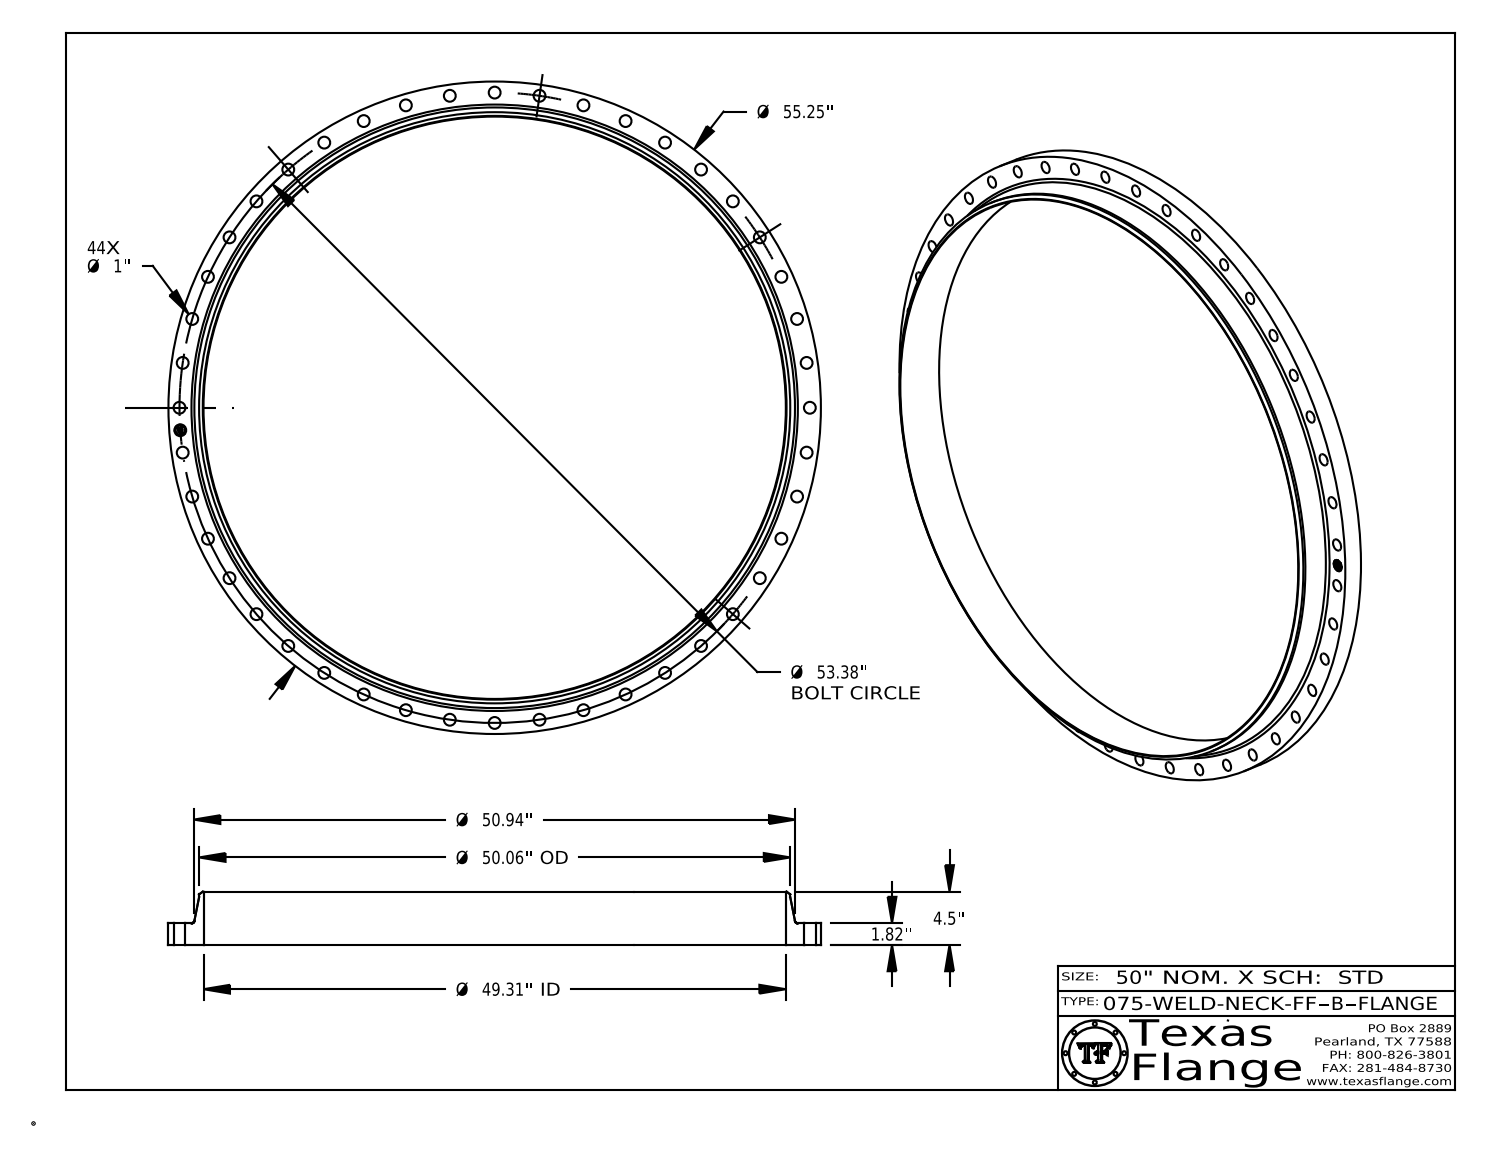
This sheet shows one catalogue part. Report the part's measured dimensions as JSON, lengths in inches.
{"part_name": "075-WELD-NECK-FF, Series B", "step_written_by": "CATIA V5 STEP AP214 (AUTOMOTIVE_DESIGN)", "units": "inches", "bodies": {"solids": 1, "faces": 488, "planar": 368, "cylindrical": 114, "other": 6}, "overall_size": [55.25, 55.25, 4.5], "volume_in3": 1054, "surface_area_in2": 2497, "round_holes": [[1, 45], [49.31, 1]], "round_bosses_or_shafts": [[0.061, 8], [55.25, 1], [50.06, 1], [0.788, 1]], "face_to_face_distances": [1.82, 4.5, 2.68, 1.805, 0.015, 2.695, 0.298, 0.292, 0.054, 0.193], "hole_center_spacings": [26.69, 7.597, 52.837, 15.039, 51.218, 3.808, 50.015, 52.16]}
